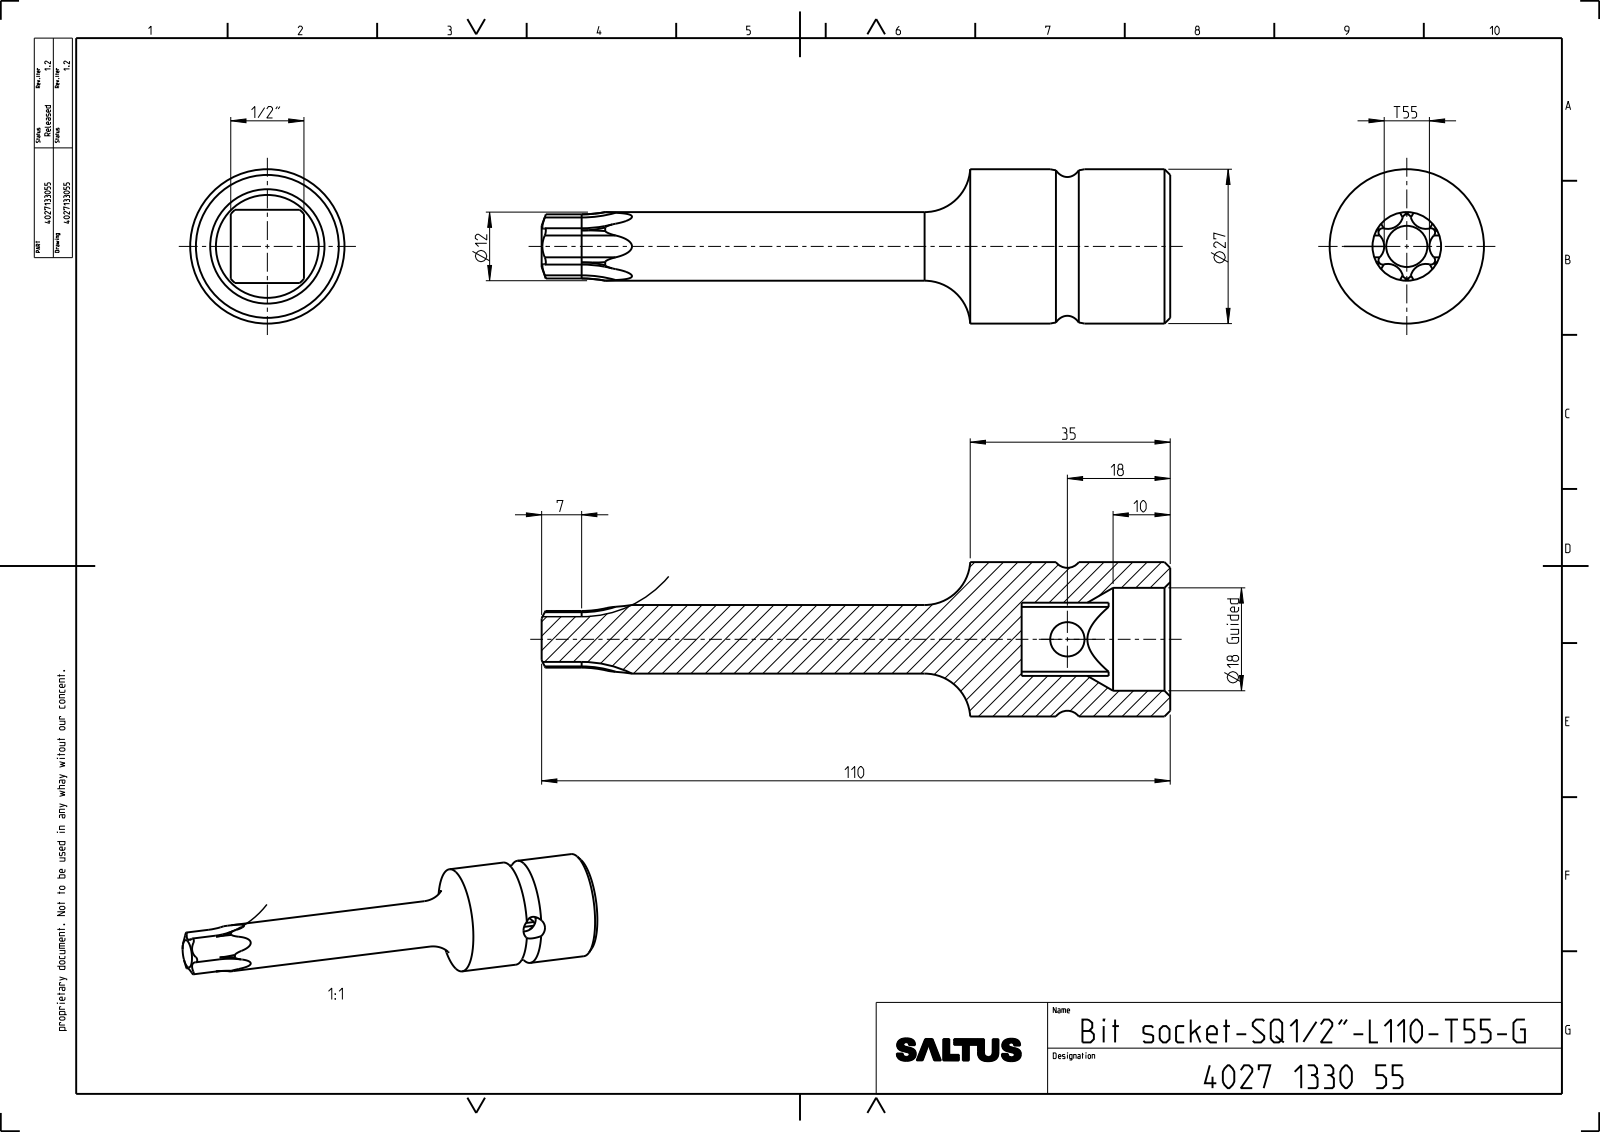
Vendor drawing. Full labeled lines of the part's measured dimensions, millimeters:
Part name (STEP PRODUCT): 4027133055
STEP written by: CREO PARAMETRIC BY PTC INC, 2022414 (CONFIG_CONTROL_DESIGN)
Units: millimetres
Bodies: 1 solid, 71 faces (7 planar, 28 cylindrical, 36 other)
Overall size (bounding box): 110 × 27 × 27
Volume: 22 647 mm³ · Surface area: 8 174 mm²
Round holes (diameter × count): ⌀6 ×1, ⌀18 ×1
Round bosses / shafts (diameter × count): ⌀27 ×1, ⌀12 ×1
Partial cylindrical surfaces — rounded edges, fillets, slot ends (radius × count): R0.74 ×6, R2.71 ×6, R8.55 ×1
Main face-to-face distances: 12.8, 26, 110, 84
